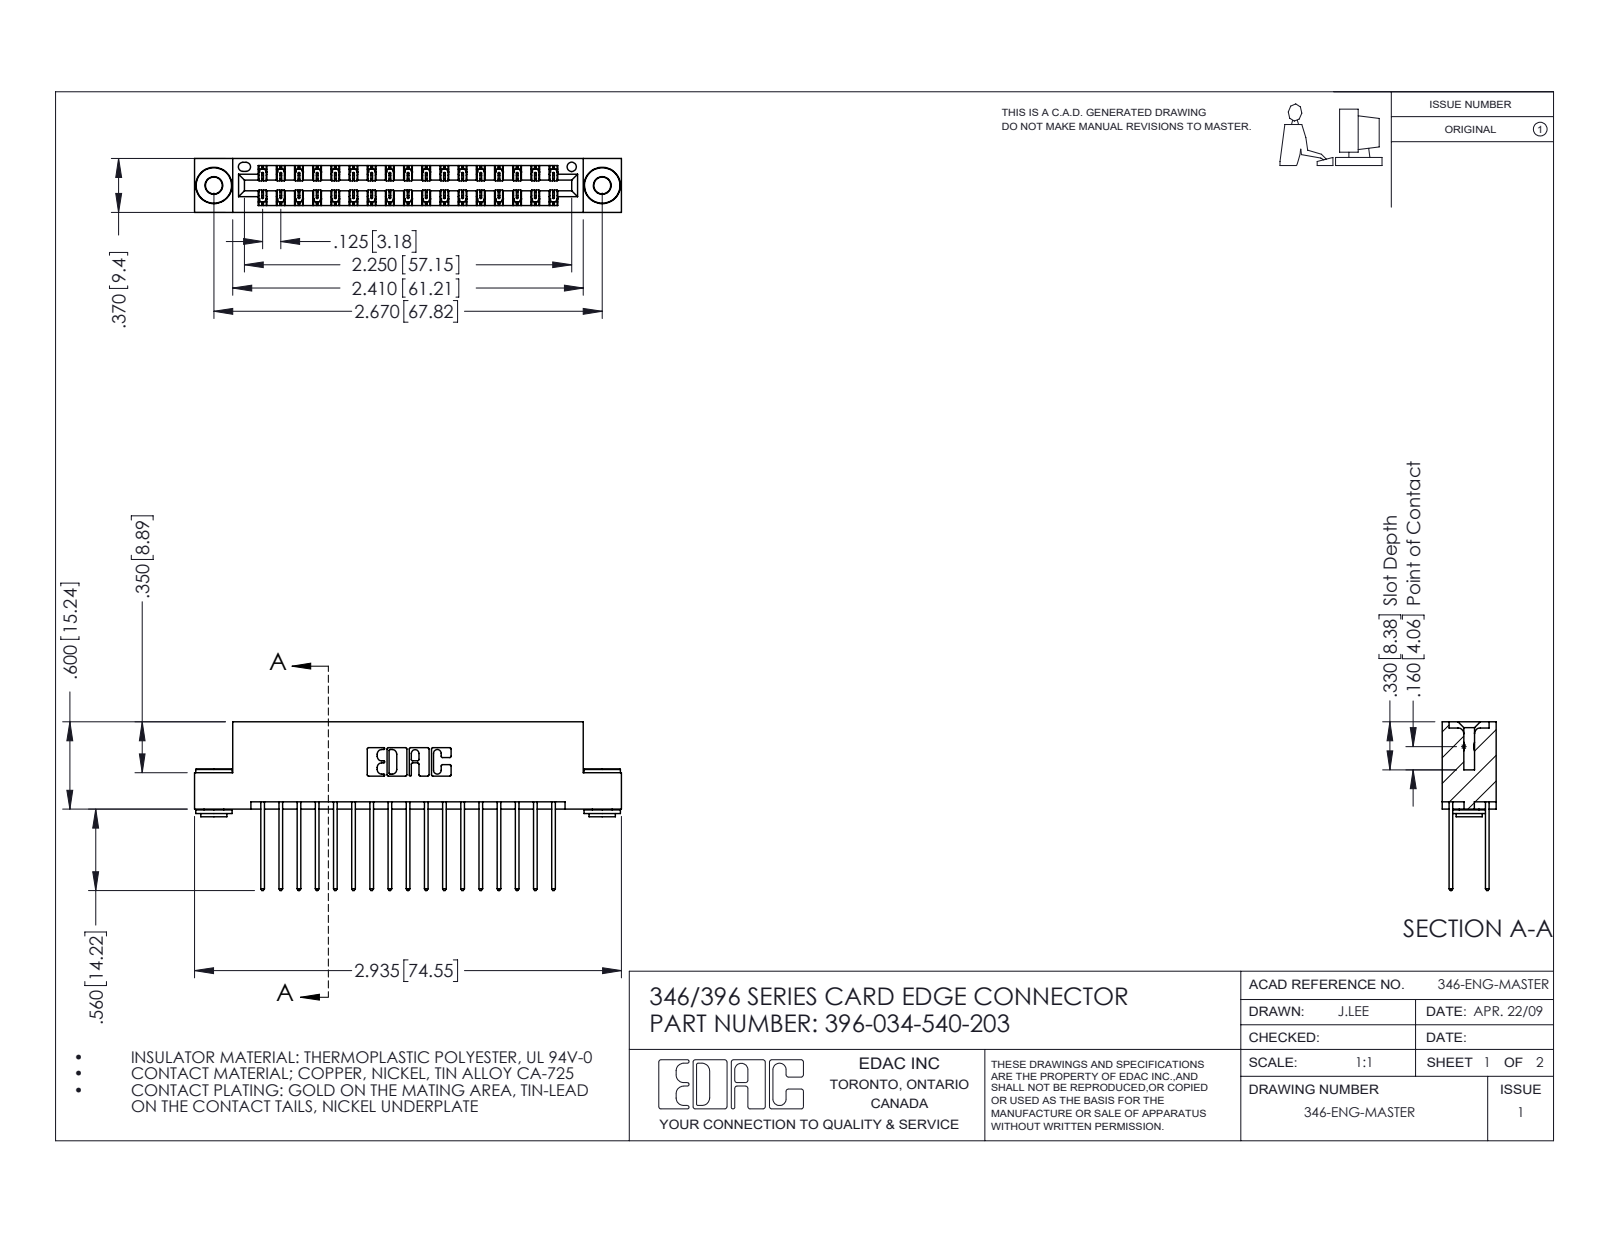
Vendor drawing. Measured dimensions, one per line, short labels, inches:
name: 345-292-001_345-293-140; 396-034-540-203; 346 Part_Flush Mounting Lugs - 0.156 Dia-TH; 345-250-002_345-250-002-102
written by: SolidWorks 2016 (CONFIG_CONTROL_DESIGN)
unit: in
bodies: 37 solids, 1928 faces (1276 planar, 644 cylindrical, 8 other)
size: 2.935 × 1.16 × 0.37
volume: 0.441 in³; area: 16.06 in²
holes: 2× ⌀0.116, 2× ⌀0.156, 1× ⌀0.064
bosses: 2× ⌀0.25, 2× ⌀0.18, 2× ⌀0.136
rounds: 51× R0.006, 34× R0.01, 22× R0.01, 6× R0.007, 6× R0.031, 3× R0.026, 2× R0.014, 2× R0.022
face distances: 0.048, 0.322, 0.25, 0.37, 0.025, 0.072, 0.298, 0.275, 0.148, 0.222
hole spacings: 0.246, 2.463, 2.67
